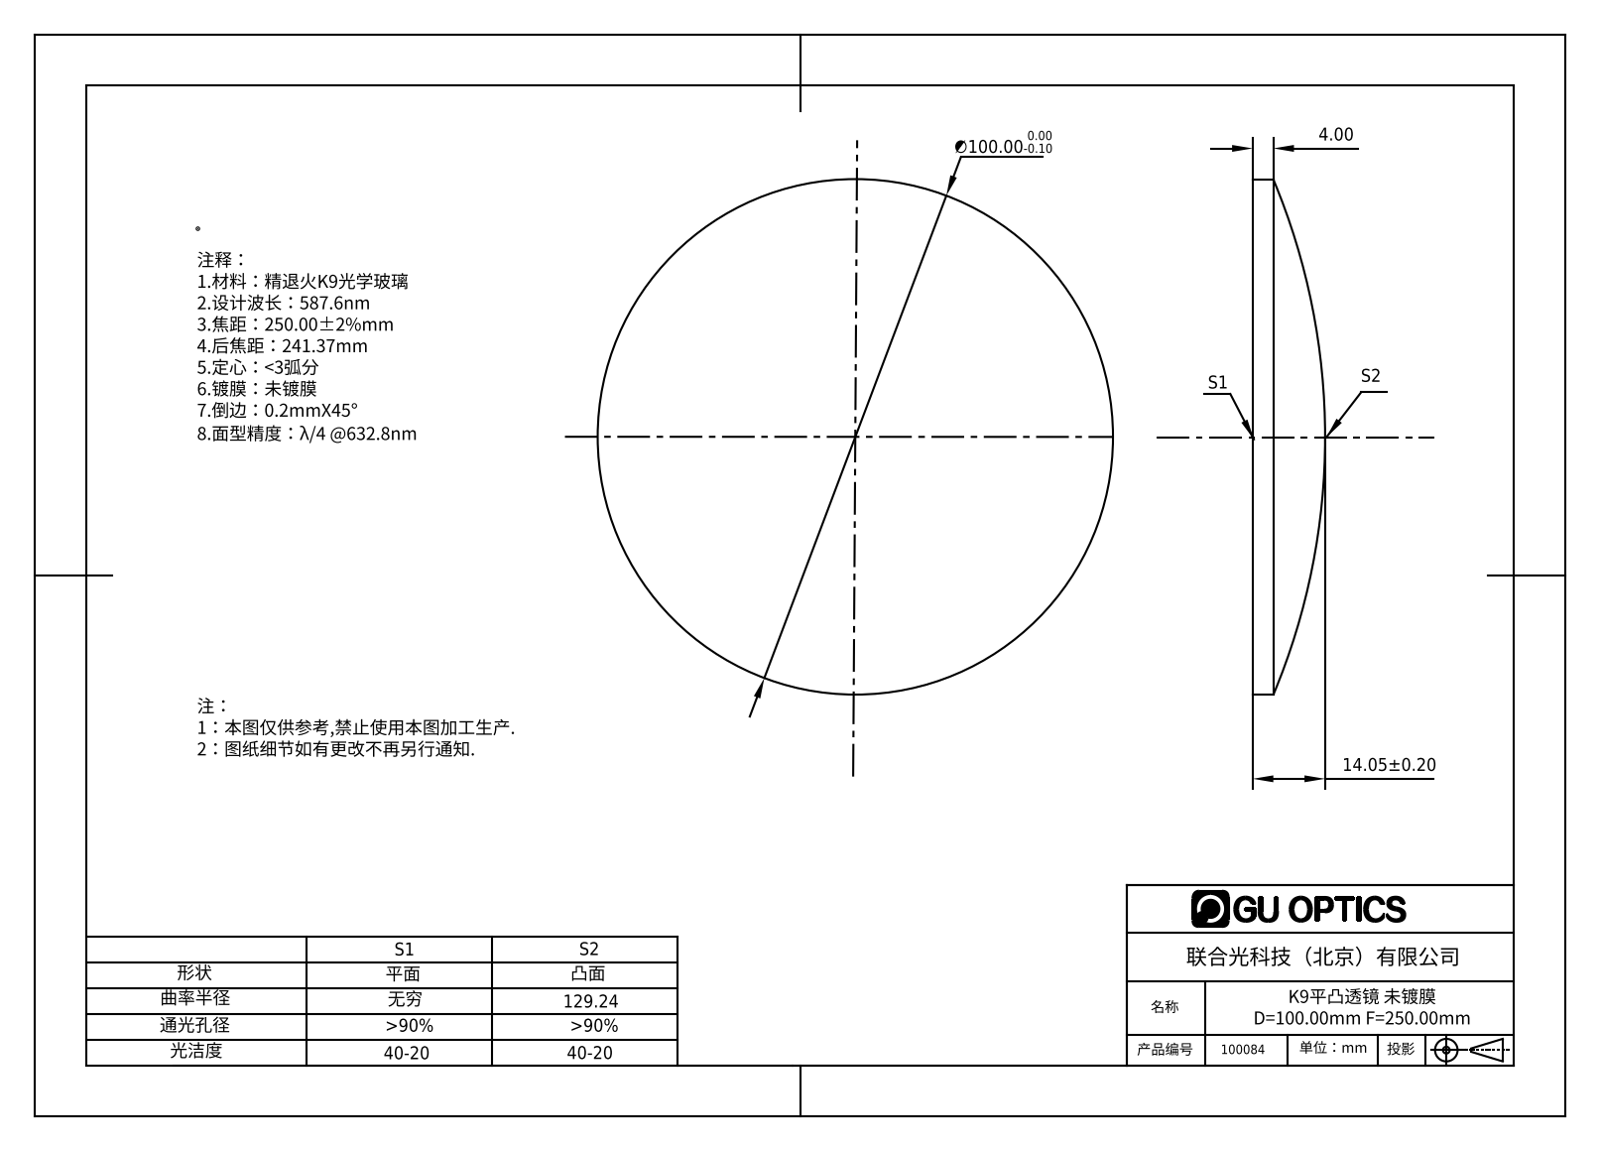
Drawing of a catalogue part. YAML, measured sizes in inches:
part_name: "100084"
step_written_by: "SolidWorks 2016 (AUTOMOTIVE_DESIGN)"
units: inches
bodies: {solids: 1, faces: 5, planar: 1, cylindrical: 2, other: 2}
overall_size: [3.937, 3.937, 0.553]
volume: 4.358
surface_area: 26.79
round_bosses_or_shafts:
  - {diameter: 3.937, count: 1}
